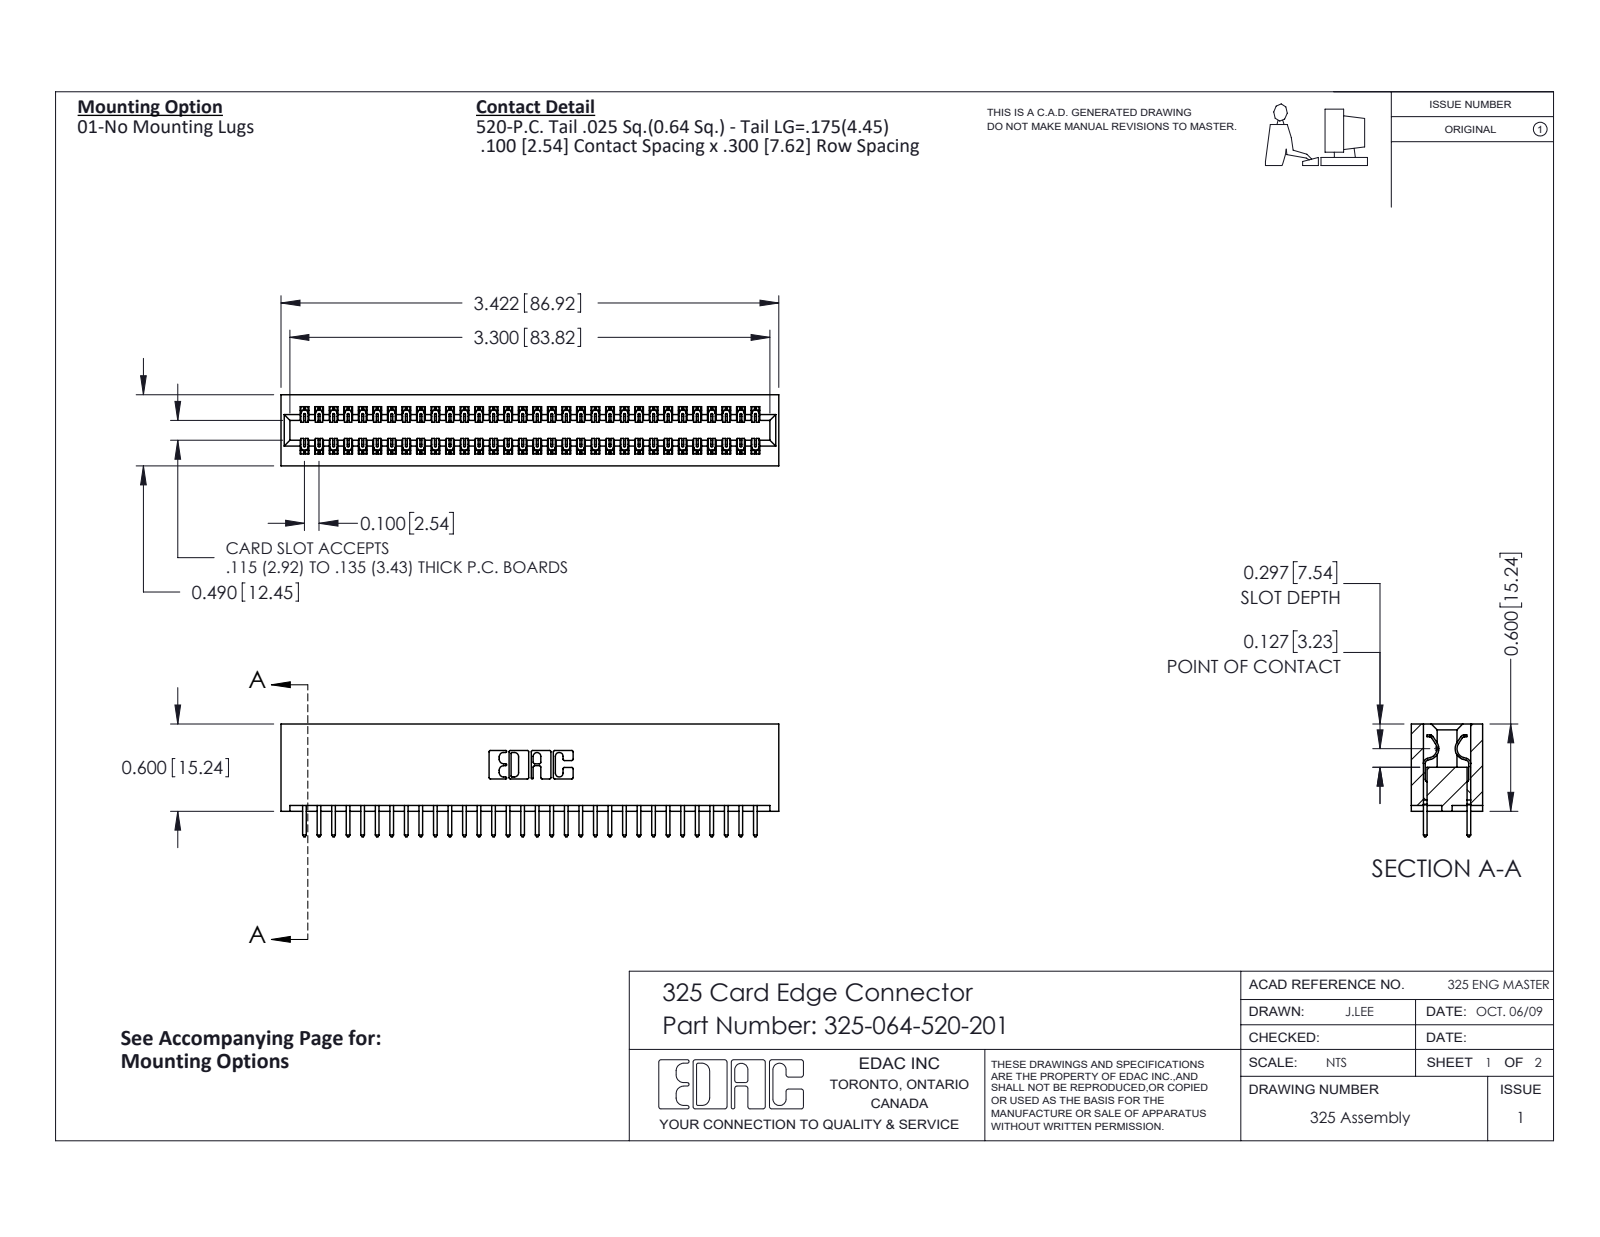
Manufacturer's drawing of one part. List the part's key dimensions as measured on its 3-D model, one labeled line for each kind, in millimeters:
Part name (STEP PRODUCT): 325 Part_Lugless; 325-064-520-201; 325-292-001_325-293-120
STEP written by: SolidWorks 2016 (CONFIG_CONTROL_DESIGN)
Units: millimetres
Bodies: 65 solids, 3434 faces (2370 planar, 1064 cylindrical, 0 other)
Overall size (bounding box): 86.9 × 19.7 × 12.4
Volume: 11 700 mm³ · Surface area: 14 490 mm²
Partial cylindrical surfaces — rounded edges, fillets, slot ends (radius × count): R0.2 ×96, R0.3 ×64, R0.3 ×22, R0.2 ×6, R0.8 ×6, R0.7 ×3, R0.4 ×2, R0.6 ×2
Main face-to-face distances: 2.1, 10.3, 7.6, 12.4, 2.7, 9.7, 0.6, 8.3, 2.5, 7
